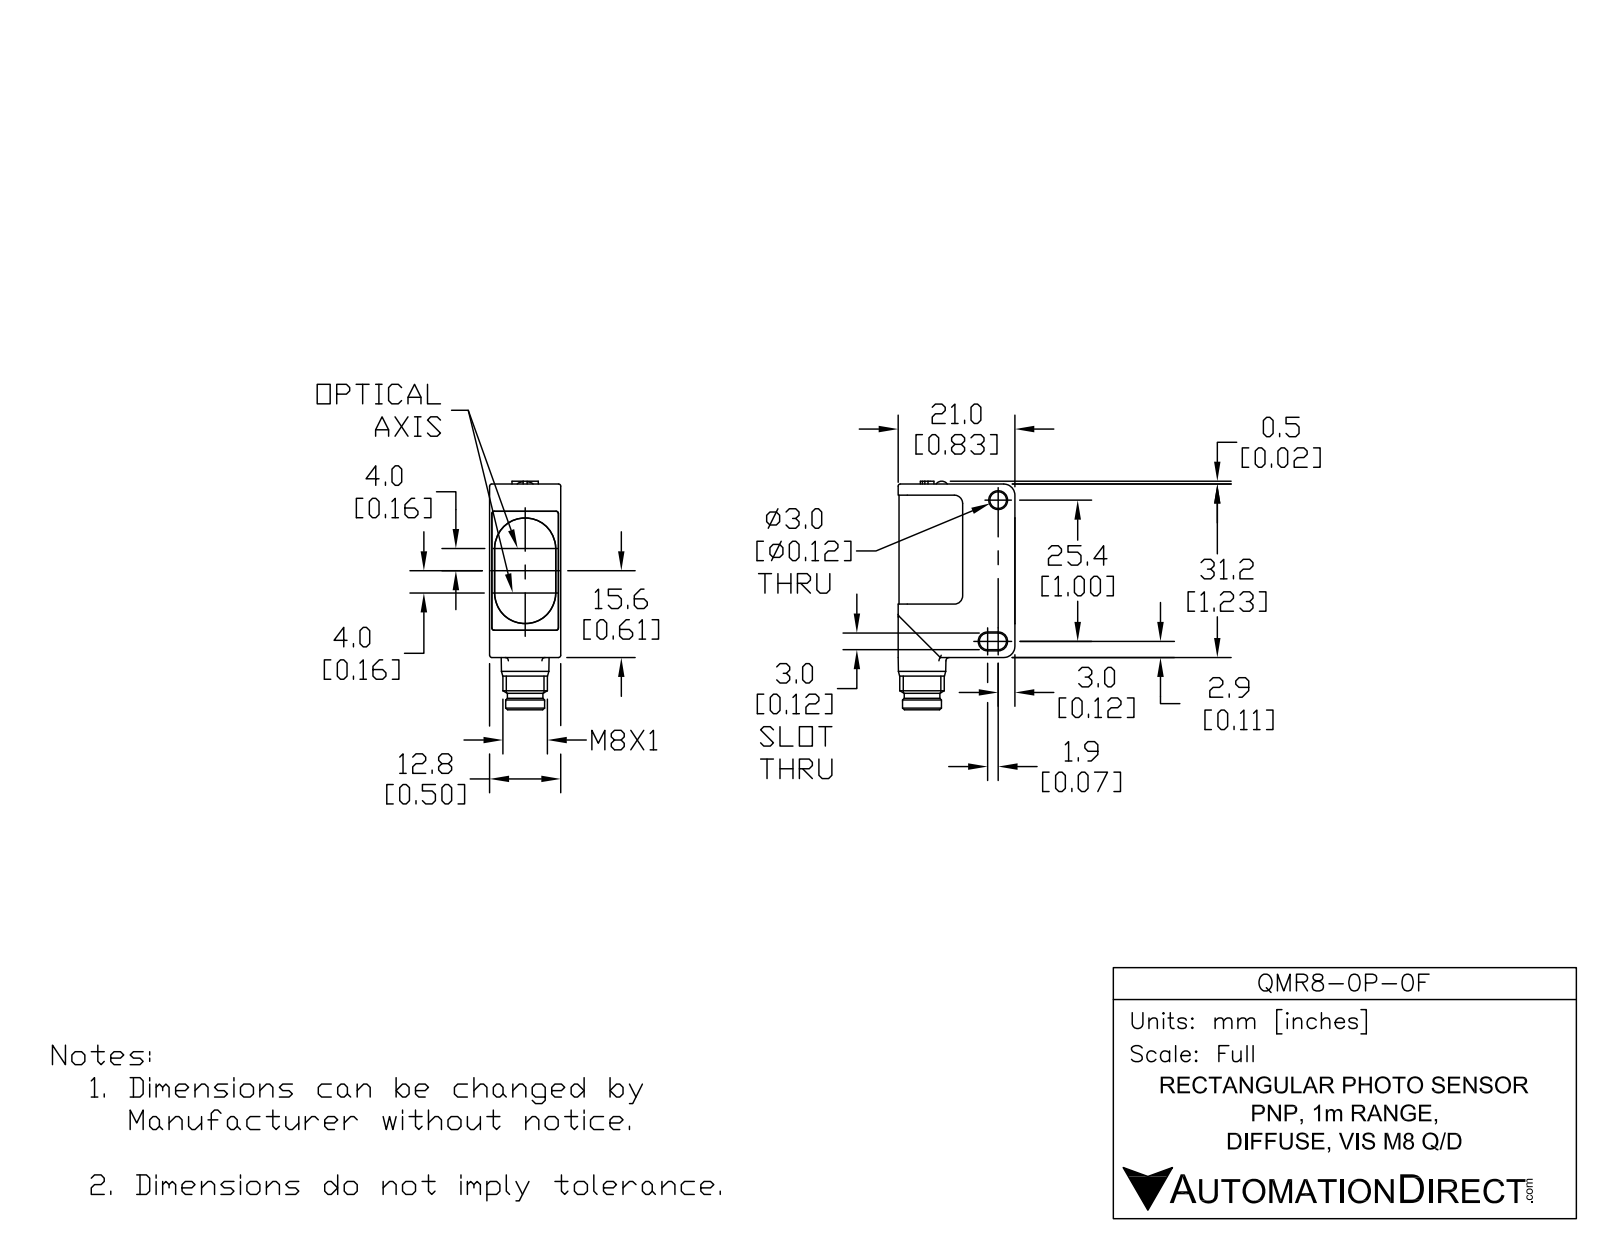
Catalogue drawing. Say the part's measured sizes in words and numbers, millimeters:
The part is named "QMR8-0P-0F". Its 3-D file was written by "SolidWorks 2017 (AUTOMOTIVE_DESIGN)". It is 7 solids with 272 faces: 125 planar, 100 cylindrical and 47 other. Overall it measures 41.1 by 21 by 12.8 millimeters. Its volume is 7 770 cubic millimeters and its surface area 4 999 square millimeters. Round holes: 3 of diameter 3, 1 of diameter 5.8. Round bosses or shafts: 4 of diameter 1, 2 of diameter 3.5, 1 of diameter 8, 1 of diameter 7, 1 of diameter 6.4. Partial cylindrical surfaces (rounded edges, fillets, slot ends): 10 of radius 0.4, 9 of radius 0.5, 6 of radius 1.5, 4 of radius 0.6, 4 of radius 1, 2 of radius 0.2, 2 of radius 1.1, 2 of radius 1.7. The main face-to-face distances are 12.6, 0.5, 12.8, 2.8, 0.4, 12.5, 12.4, 12.2, 1.5, 18.1. The hole center spacings are 1, 5.2, 6.2.
